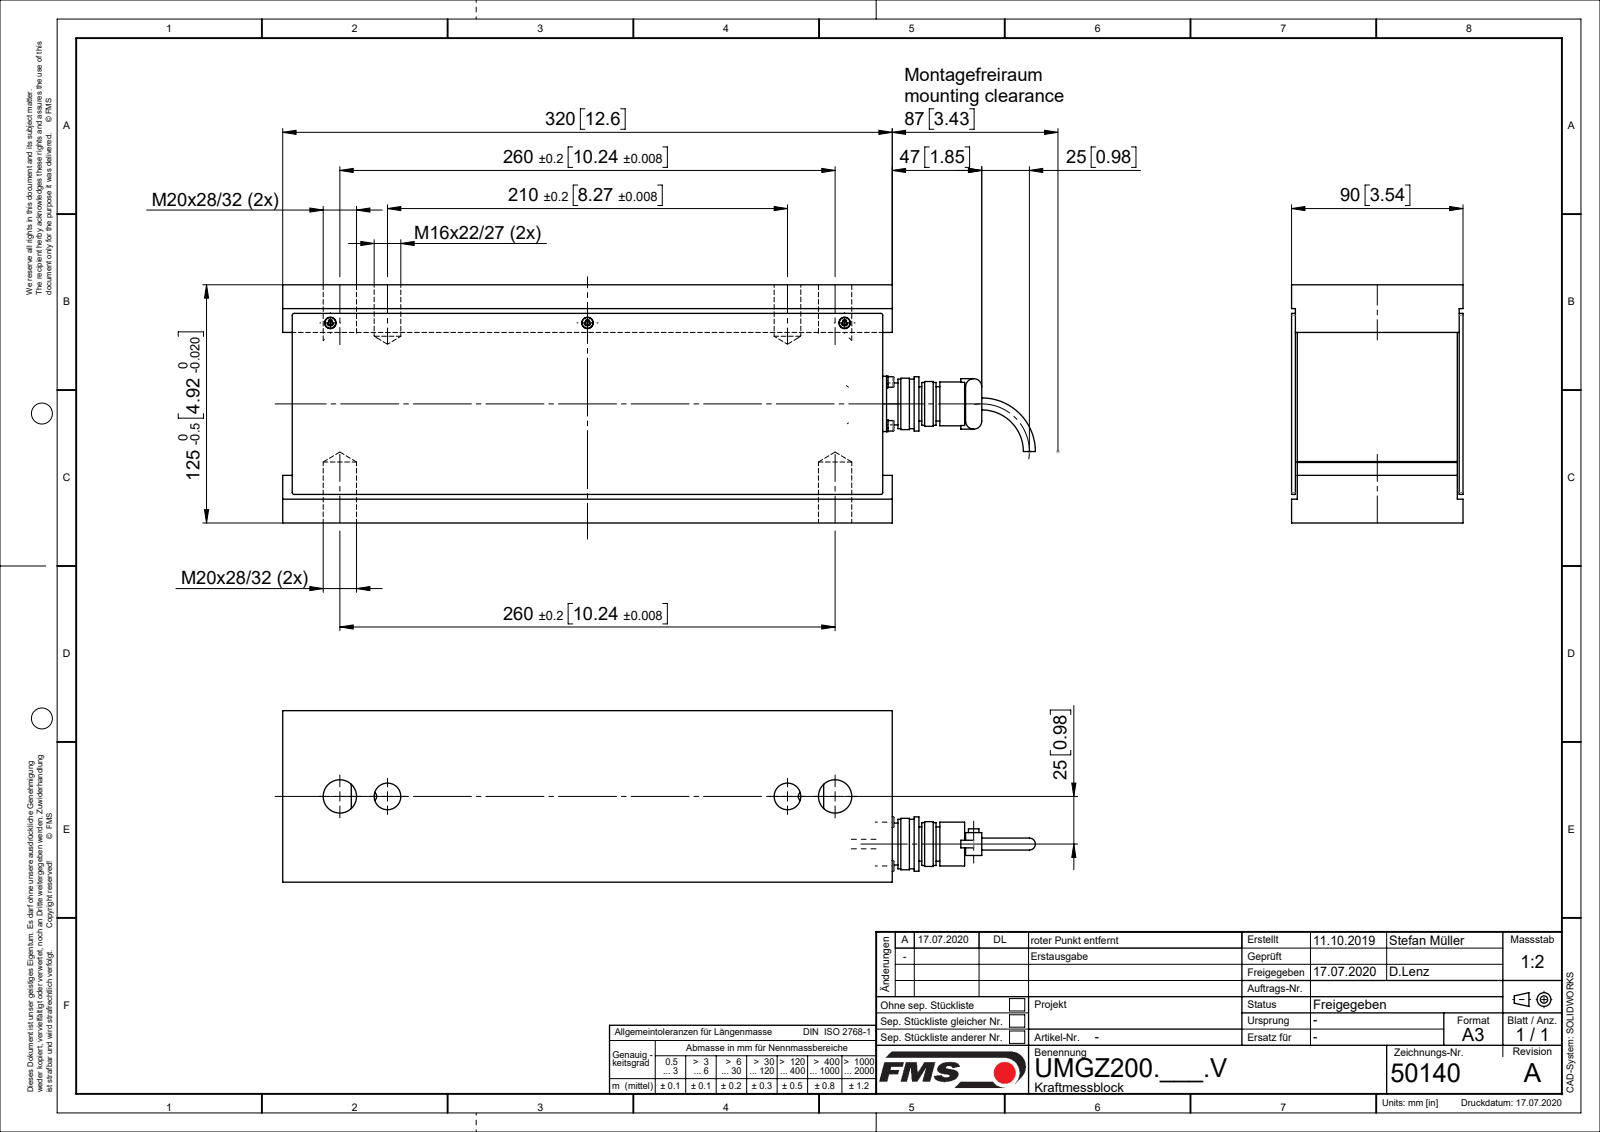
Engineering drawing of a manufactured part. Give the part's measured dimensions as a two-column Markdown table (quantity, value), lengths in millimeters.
| quantity | value |
| --- | --- |
| part name | U50140; U4945804; TEIL1; KABELDOSE_PG_AMPH_4-POL (+4 more) |
| STEP written by | Mechanical Desktop 2007 (CONFIG_CONTROL_DESIGN) |
| units | millimeters |
| bodies | 12 solids, 281 faces (79 planar, 136 cylindrical, 66 other) |
| overall size | 418 × 125 × 90 |
| volume | 3 453 000 mm³ |
| surface area | 306 811 mm² |
| round holes (diameter × count) | 2.6 × 7, 3.2 × 4, 3.6 × 3, 6 × 3, 14.21 × 2, 17.74 × 2 |
| round bosses / shafts (diameter × count) | 6.2 × 4, 5.5 × 4, 3 × 4, 2.5 × 4, 28 × 1, 23 × 1, 22 × 1, 21 × 1 |
| partial cylindrical surfaces (radius × count) | 4 × 4 |
| main face-to-face distances | 2, 88, 85, 3, 1, 87, 90, 86, 125, 84 |
| hole center spacings | 23, 25, 32.53, 135, 235, 210, 260, 270 |
